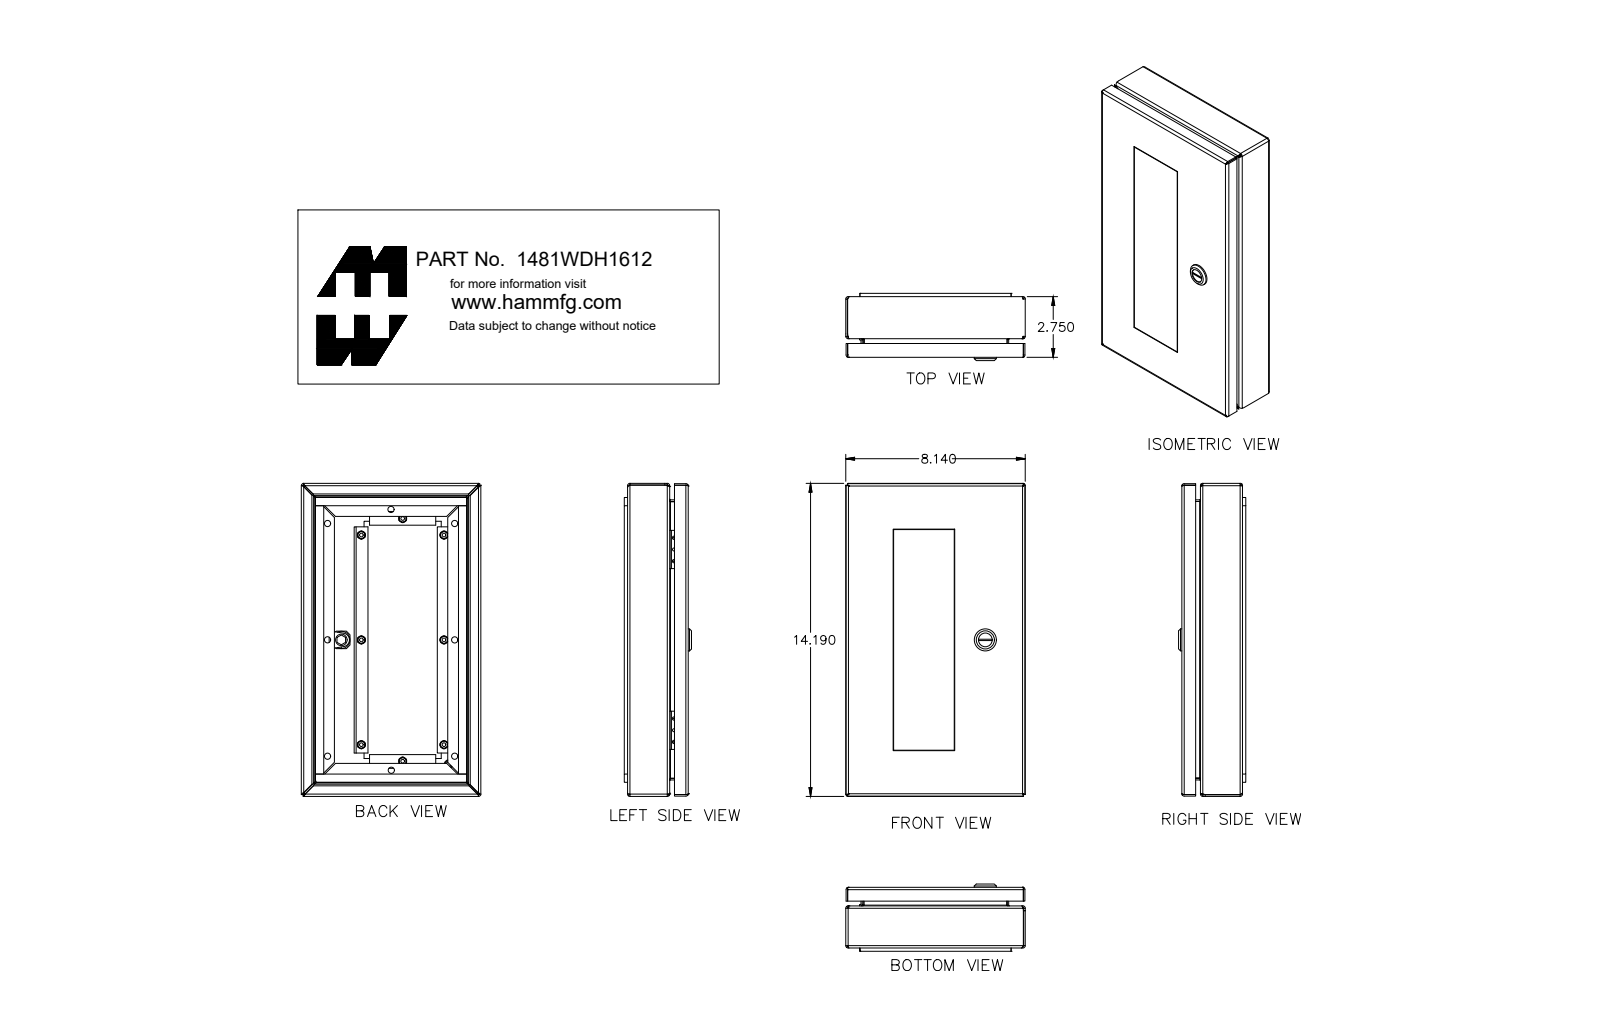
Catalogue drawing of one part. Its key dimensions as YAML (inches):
part_name: "1481WDH1612_Default"
step_written_by: "SolidWorks 2019 (CONFIG_CONTROL_DESIGN)"
units: inches
bodies: {solids: 35, faces: 860, planar: 465, cylindrical: 245, other: 150}
overall_size: [14.19, 8.14, 2.91]
volume: 32.53
surface_area: 779.1
round_holes:
  - {diameter: 0.281, count: 8}
  - {diameter: 0.13, count: 6}
  - {diameter: 0.136, count: 2}
  - {diameter: 0.232, count: 1}
  - {diameter: 0.24, count: 1}
  - {diameter: 0.242, count: 1}
  - {diameter: 0.625, count: 1}
  - {diameter: 0.785, count: 1}
round_bosses_or_shafts:
  - {diameter: 0.226, count: 8}
  - {diameter: 0.164, count: 8}
  - {diameter: 0.368, count: 6}
  - {diameter: 1.1, count: 1}
  - {diameter: 0.785, count: 1}
  - {diameter: 0.525, count: 1}
  - {diameter: 0.455, count: 1}
  - {diameter: 0.398, count: 1}
partial_cylinders:
  - {radius: 0.036, count: 28}
  - {radius: 0.108, count: 28}
  - {radius: 0.101, count: 16}
  - {radius: 0.016, count: 4}
  - {radius: 0.088, count: 4}
  - {radius: 0.125, count: 2}
  - {radius: 0.021, count: 1}
  - {radius: 0.029, count: 1}
face_to_face_distances: [0.072, 0.25, 2.578, 0.178, 0.842, 1.736, 8.068, 2.328, 0.592, 2.678]
hole_center_spacings: [2.951, 11.545, 5.764, 3.75, 4.75, 5.273, 5.273, 6.052]
